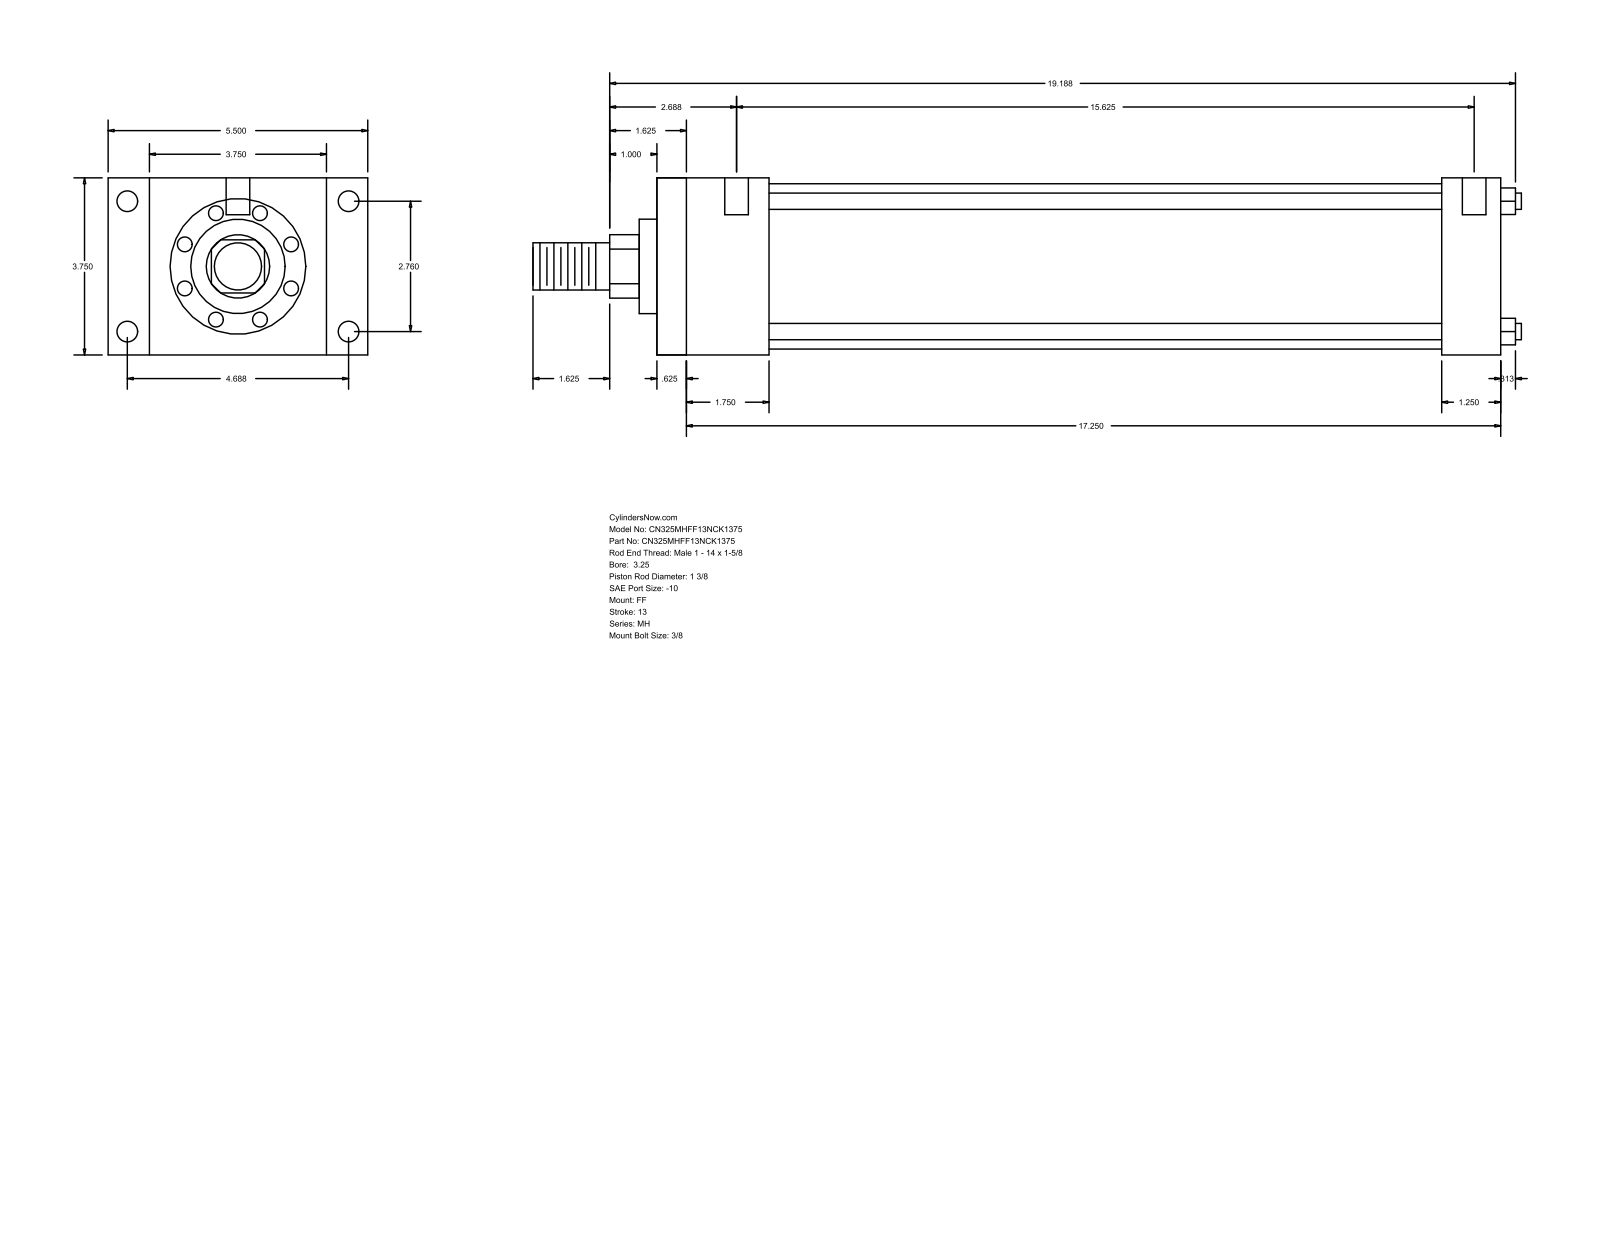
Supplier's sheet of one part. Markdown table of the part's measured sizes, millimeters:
| quantity | value |
| --- | --- |
| part name | MH_FF__0325_1.375 |
| STEP written by | GSSL Pune (CONFIG_CONTROL_DESIGN) |
| units | millimeters |
| bodies | 0 solids, 92 faces (64 planar, 28 cylindrical, 0 other) |
| overall size | 531.81 × 139.7 × 95.25 |
| round holes (diameter × count) | 5.56 × 4, 11.13 × 4, 12.7 × 2 |
| round bosses / shafts (diameter × count) | 8.76 × 4, 88.9 × 1, 50.8 × 1, 34.92 × 1, 25.4 × 1 |
| partial cylindrical surfaces (radius × count) | 17.06 × 1 |
| main face-to-face distances | 95.24, 454.03, 15.87, 438.16, 22.23, 117.47, 422.28, 406.41, 31.75, 60.32 |
| hole center spacings | 70.1, 119.06, 138.16, 403.23, 1.59, 4.76, 396.88, 398.47 |
